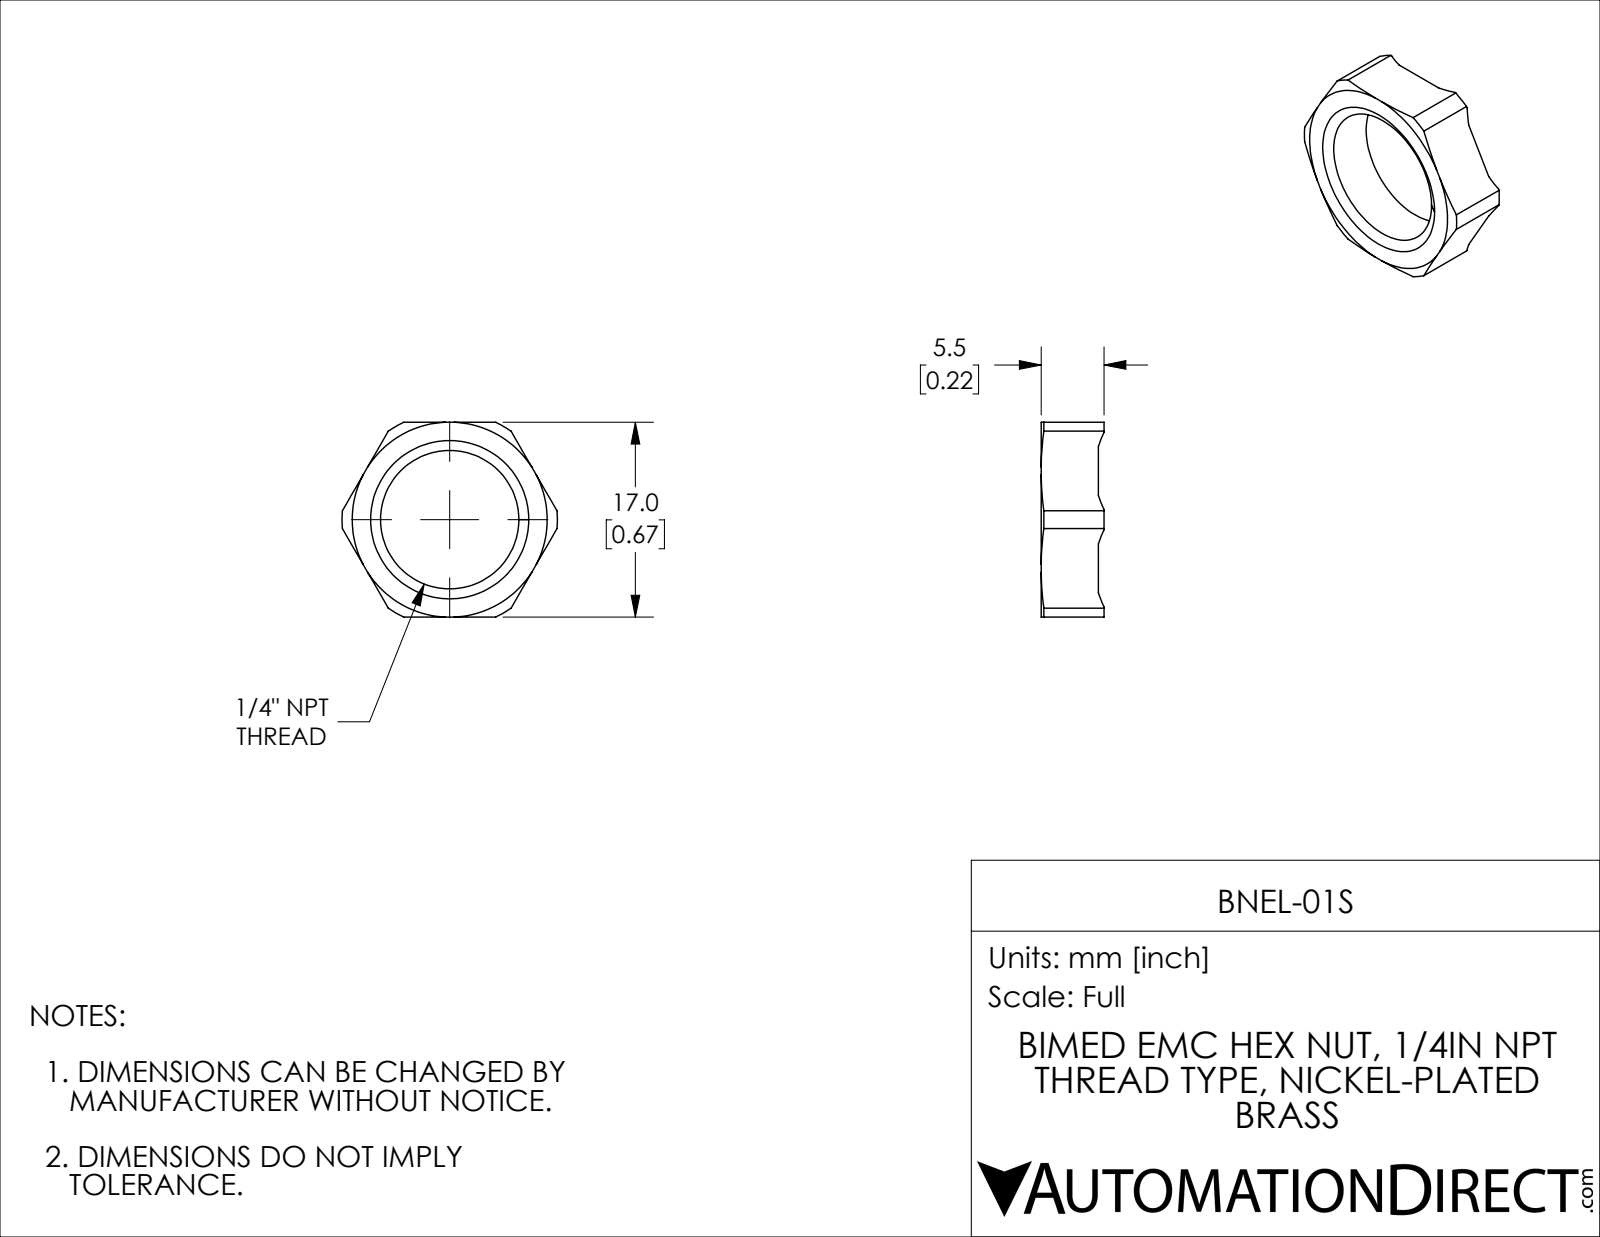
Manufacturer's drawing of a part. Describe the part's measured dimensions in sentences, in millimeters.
The part is named "BNEL-01S". Its 3-D file was written by "SolidWorks 2021 (CONFIG_CONTROL_DESIGN)". It is 1 solid with 46 faces: 14 planar, 8 cylindrical and 24 other. Overall it measures 18.8 by 17 by 5.5 millimeters. Its volume is 652 cubic millimeters and its surface area 725 square millimeters. Round holes: 1 of diameter 12.08. Partial cylindrical surfaces (rounded edges, fillets, slot ends): 1 of radius 9.4. The main face-to-face distances are 17, 5, 0.5, 5.5.
